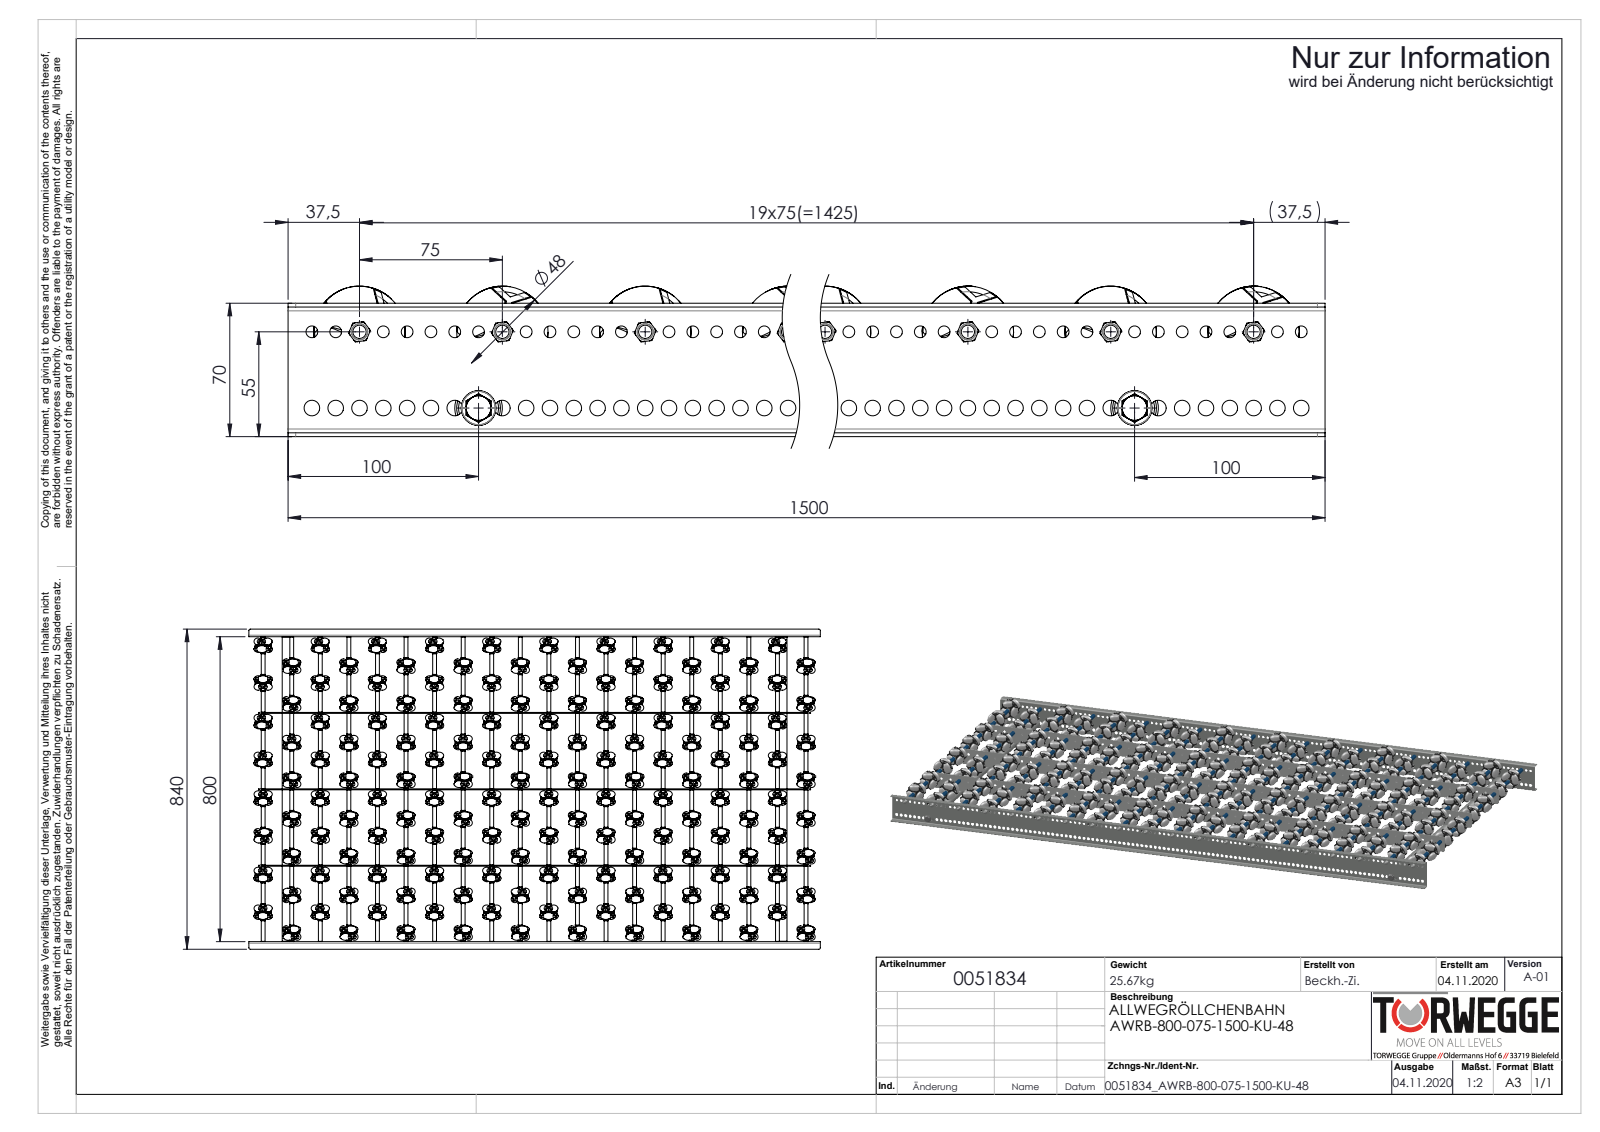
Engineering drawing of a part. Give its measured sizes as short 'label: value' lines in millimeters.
name: Traversen_KFG_L800; AWR48_Halter; S100994_Sperrzahnschraube_M08x16-8.8-A2K; AWR48_Stift (+8 more)
written by: SolidWorks 2020 (AUTOMOTIVE_DESIGN)
unit: mm
bodies: 2635 solids, 46450 faces (16178 planar, 18208 cylindrical, 12064 other)
size: 1500 × 840 × 79
volume: 8 944 000 mm³; area: 6 065 000 mm²
holes: 960× ⌀3.7, 960× ⌀4.2, 119× ⌀6.2, 119× ⌀8.2, 58× ⌀6.5, 20× ⌀4.92, 20× ⌀8.4, 2× ⌀6.8, 2× ⌀21
bosses: 960× ⌀4, 858× ⌀3.7, 22× ⌀8, 20× ⌀47.1, 20× ⌀42, 20× ⌀11, 20× ⌀10, 20× ⌀7
rounds: 8× R4, 4× R2, 4× R5
face distances: 2, 200.5, 2.5, 802, 401, 203, 198, 68, 800, 804
hole spacings: 36.05, 36.06, 99, 36.07, 122.72, 36.04, 4.65, 84.5
